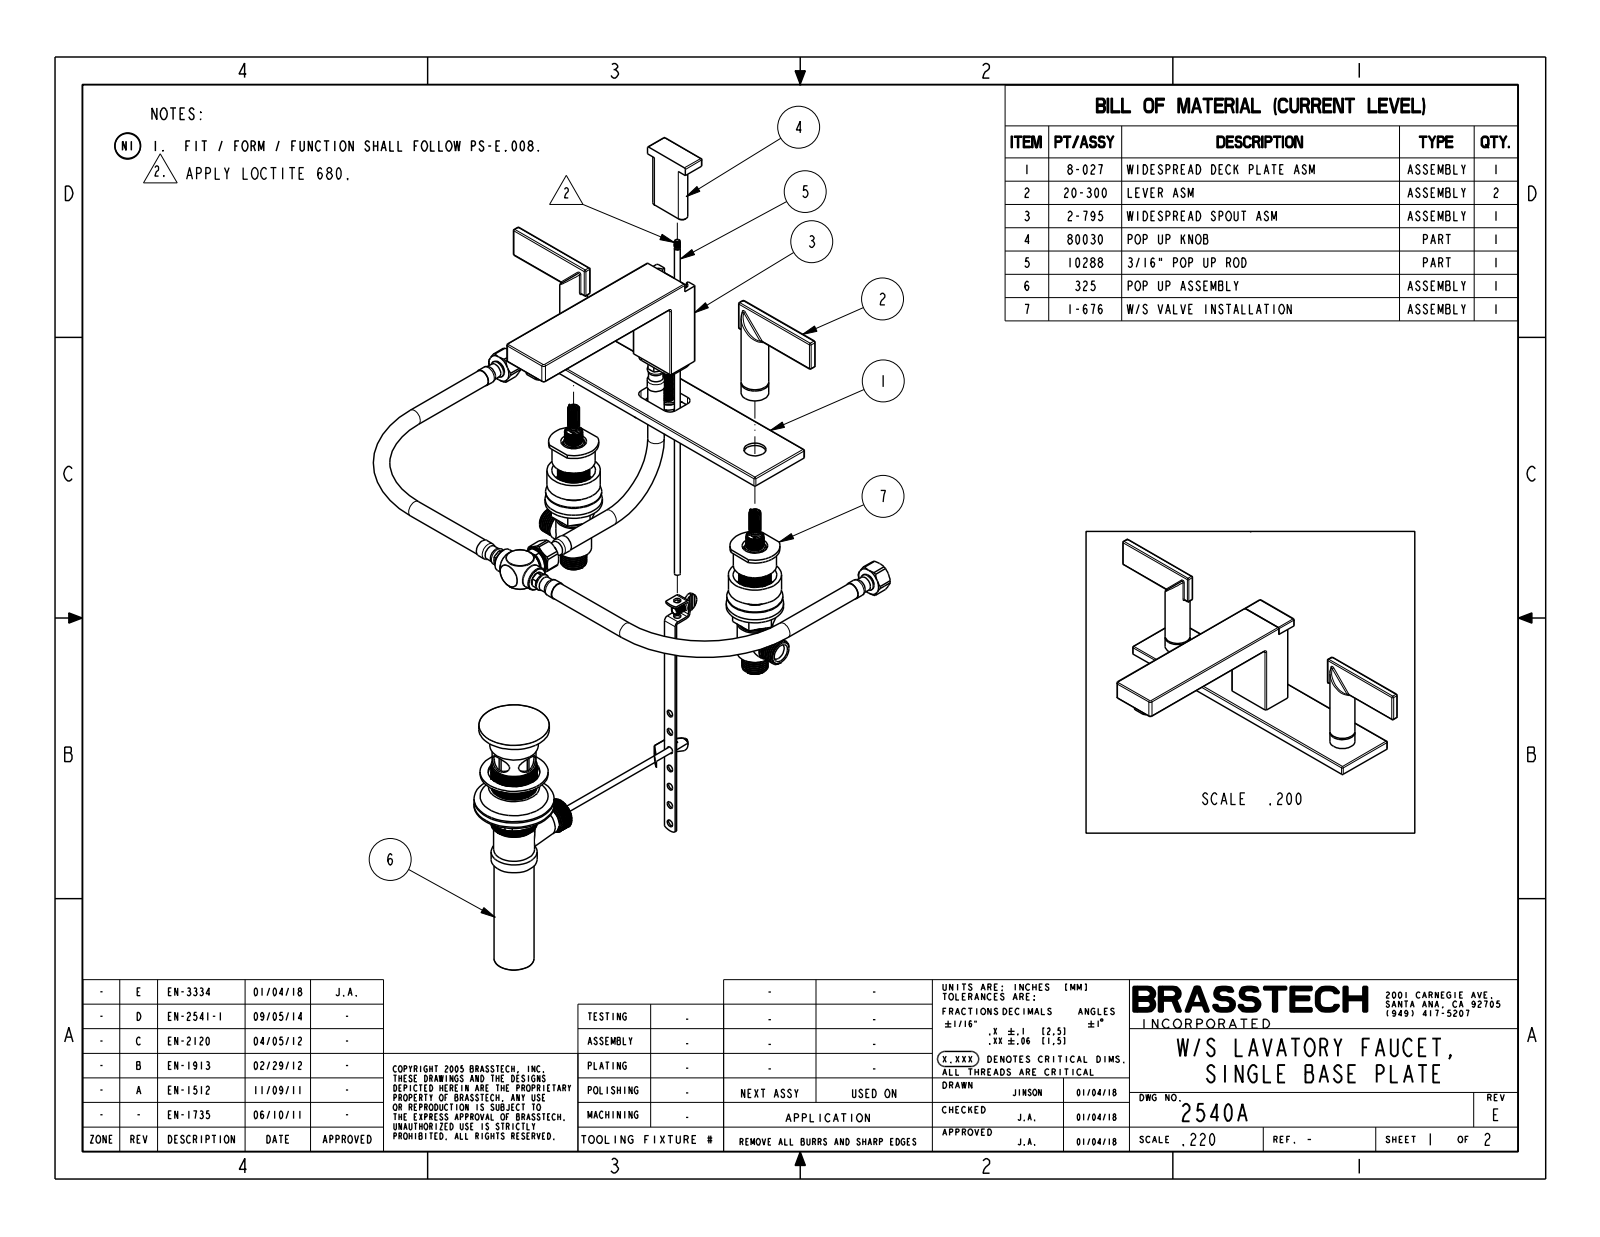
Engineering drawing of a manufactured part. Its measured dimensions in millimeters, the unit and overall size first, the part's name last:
Units: millimetres
Overall size (bounding box): 333.2 × 184.1 × 89.2
Round bosses / shafts (diameter × count): ⌀21.8 ×2, ⌀17.3 ×2, ⌀22.2 ×1
Partial cylindrical surfaces — rounded edges, fillets, slot ends (radius × count): R1 ×49, R2 ×3
Main face-to-face distances: 7.9, 87.9, 80, 10.8, 16.8, 71.3, 63.4, 16.6, 42.4, 14.1
Volume: 384 100 mm³ · Surface area: 81 420 mm²
Bodies: 1 solid, 178 faces (46 planar, 76 cylindrical, 56 other)
Part name (STEP PRODUCT): 2540A
STEP written by: CREO PARAMETRIC BY PTC INC, 2018400 (CONFIG_CONTROL_DESIGN)
